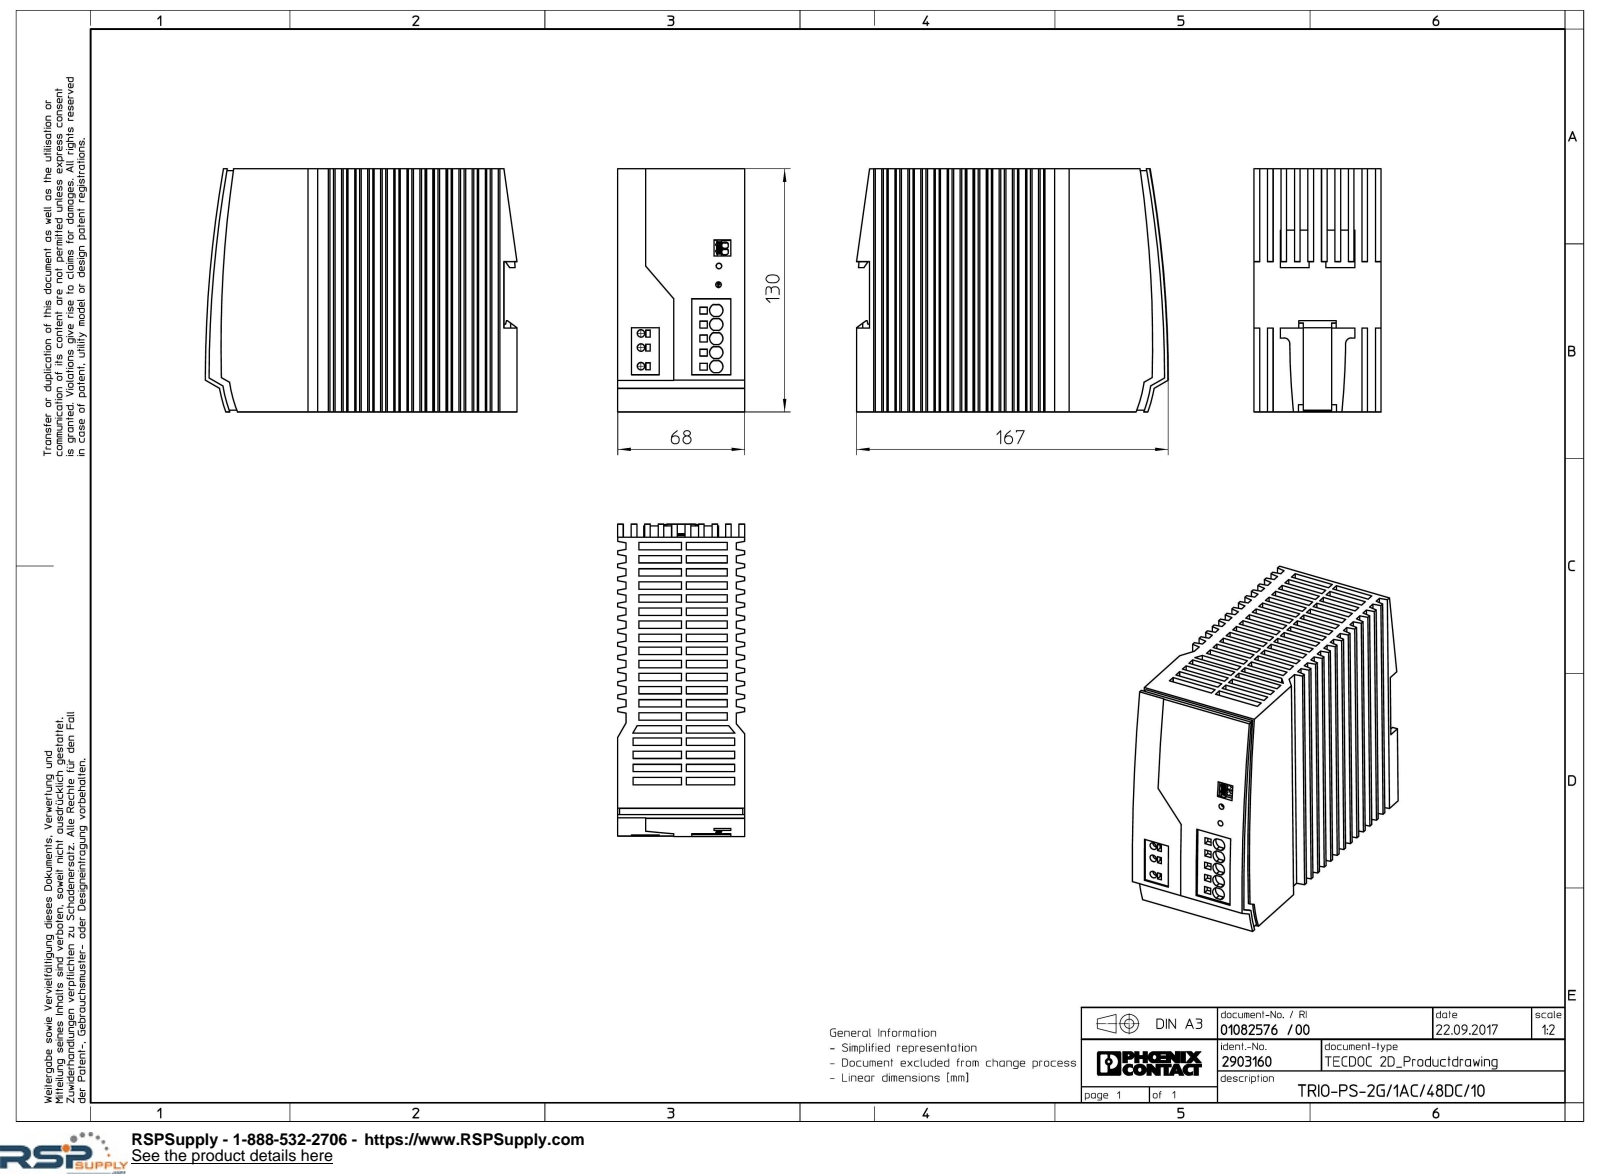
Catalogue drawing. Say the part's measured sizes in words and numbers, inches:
The part is named "TRIO_PS_2G_1AC_48DC_10-select". Its 3-D file was written by "Creo Elements/Direct Modeling 20.1A 29-Sep-2018 (C) Parametric Technology GmbH (AUTOMOTIVE_DESIGN)". It is 1 solid with 792 faces: 742 planar, 45 cylindrical and 5 other. Overall it measures 6.575 by 5.118 by 2.677 inches. Its volume is 79.21 cubic inches and its surface area 196.1 square inches. Round holes: 3 of diameter 0.157, 2 of diameter 0.118. Partial cylindrical surfaces (rounded edges, fillets, slot ends): 10 of radius 0.136, 2 of radius 0.022, 2 of radius 0.024, 2 of radius 0.041, 2 of radius 0.041, 2 of radius 0.118, 2 of radius 16.929, 1 of radius 1.575. The main face-to-face distances are 0.543, 1.086, 0.177, 2.5, 1.629, 0.271, 2.677, 0.118, 2.172, 0.272. The hole center spacings are 0.295, 0.394, 0.689.
